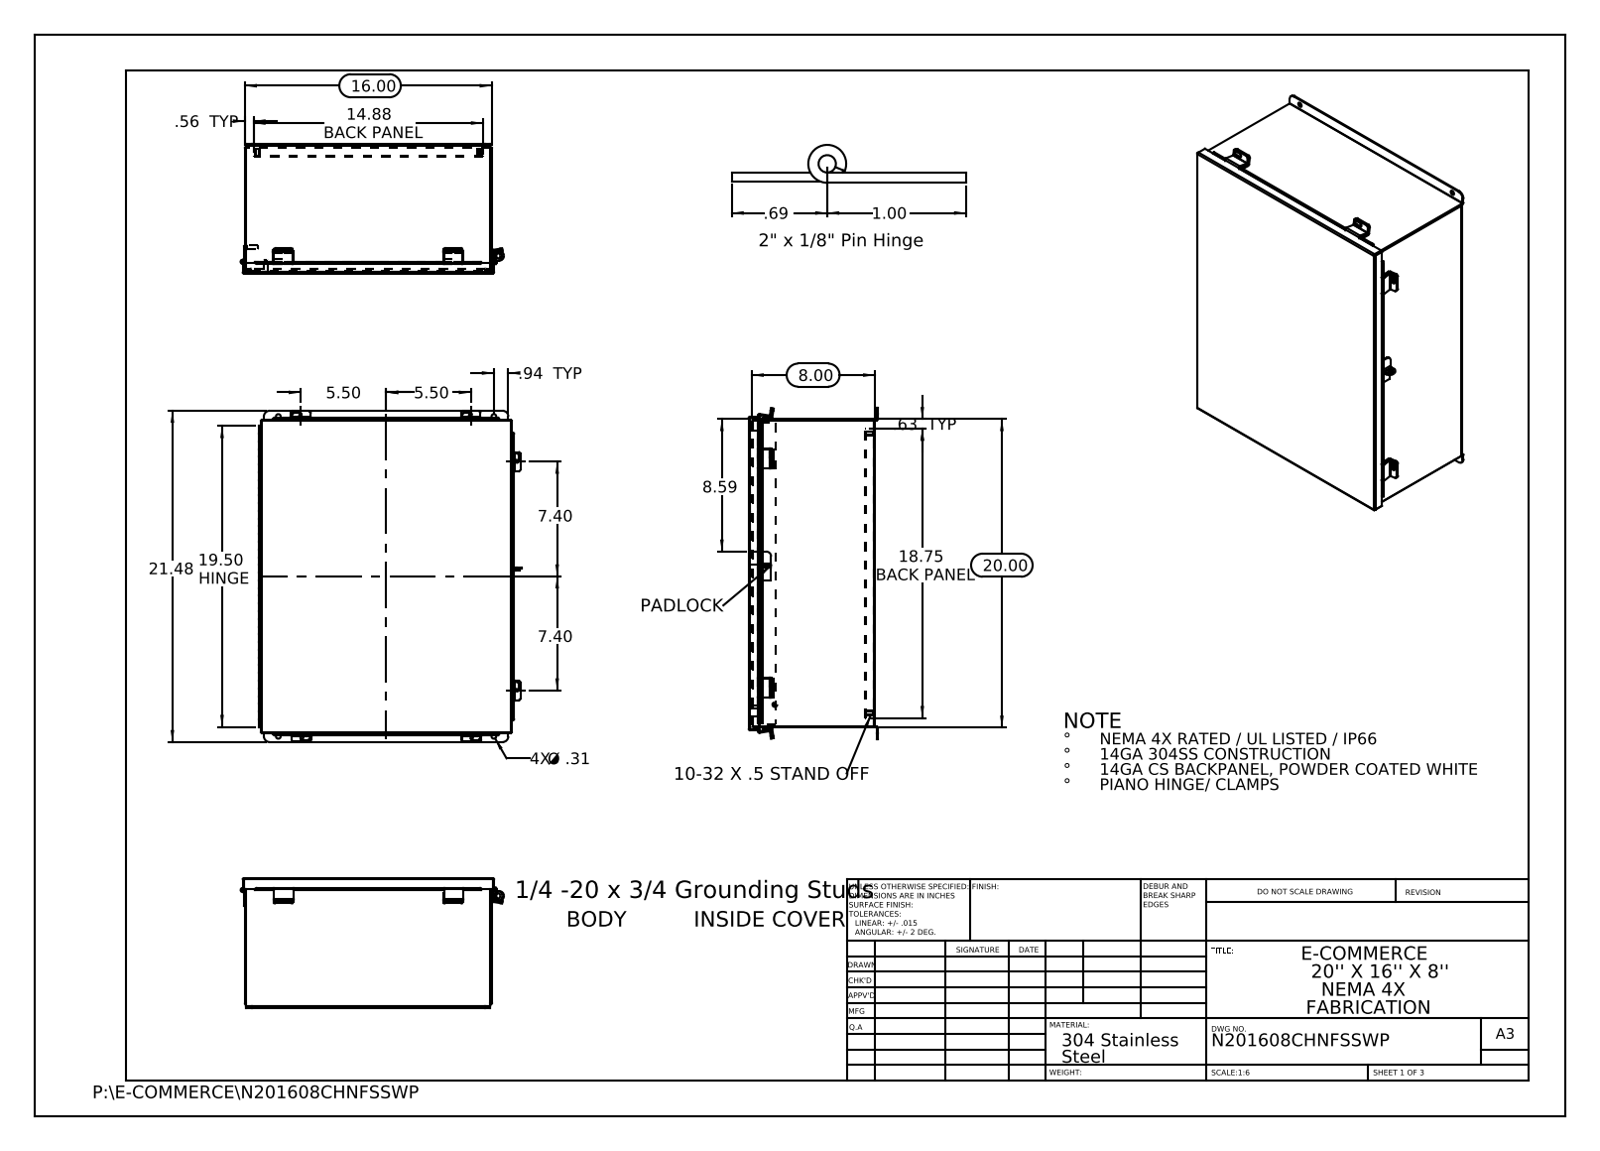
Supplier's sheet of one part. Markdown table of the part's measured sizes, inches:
| quantity | value |
| --- | --- |
| part name | N201608CHNFSSWP Hinge Cover Side JIC; N201608CHNFSSWP JIC Backpanel; N201608CHNFSSWP JIC Clamp Bracket; N201608CHNFSSWP _JIC Hinge (+8 more) |
| STEP written by | SolidWorks 2013 (CONFIG_CONTROL_DESIGN) |
| units | inches |
| bodies | 27 solids, 938 faces (579 planar, 339 cylindrical, 20 other) |
| overall size | 21.476 × 17.072 × 8.39 |
| volume | 123.6 in³ |
| surface area | 3 354 in² |
| round holes (diameter × count) | 0.25 × 10, 0.187 × 4, 0.312 × 4, 0.125 × 1, 0.125 × 1, 0.373 × 1, 0.375 × 1 |
| round bosses / shafts (diameter × count) | 0.313 × 4, 0.315 × 2, 0.236 × 2, 0.273 × 1, 0.25 × 1 |
| partial cylindrical surfaces (radius × count) | 0.125 × 24, 0.013 × 13, 0.009 × 12, 0.088 × 12, 0.133 × 12, 0.083 × 6, 0.1 × 6, 0.375 × 4 |
| main face-to-face distances | 0.075, 8.128, 8.053, 8.203, 15.925, 7.628, 0.575, 0.5, 7.553, 0.649 |
| hole center spacings | 1.315, 14.235, 19.427, 24.048, 11, 13.976, 14.375, 18.126 |
